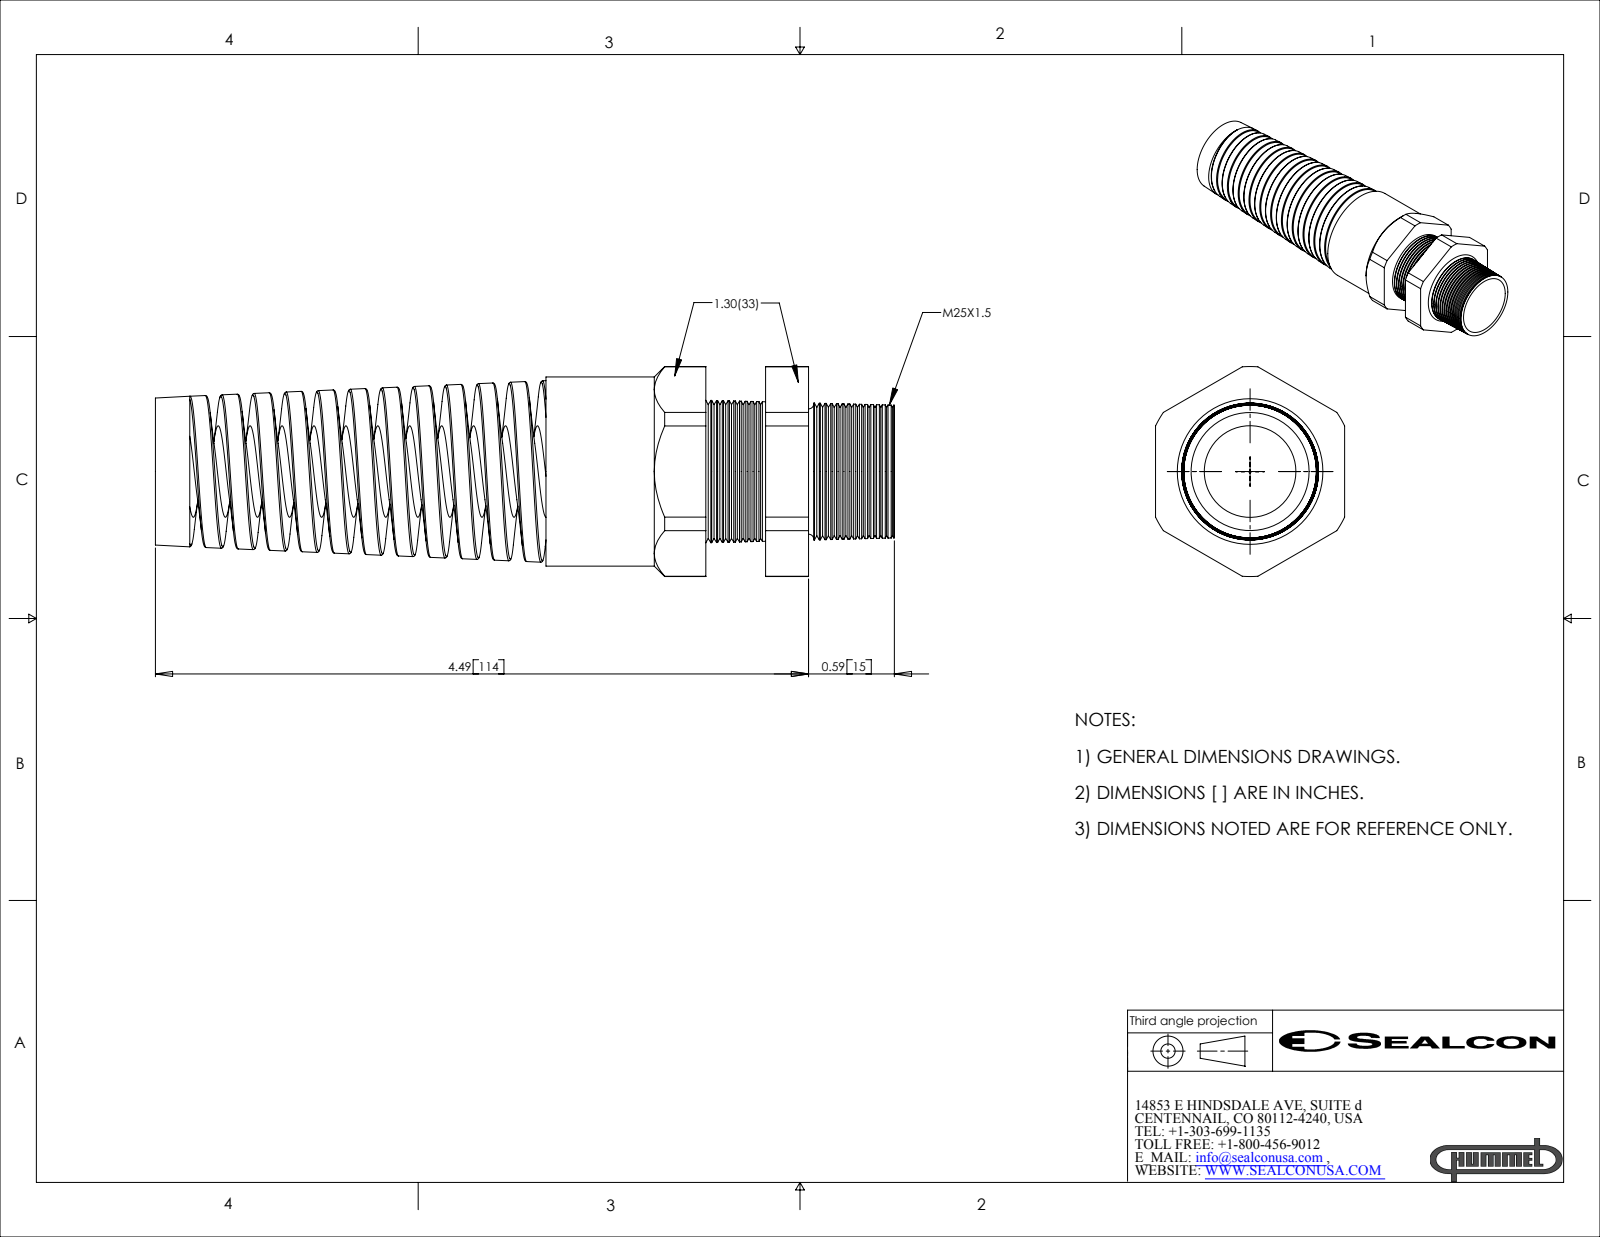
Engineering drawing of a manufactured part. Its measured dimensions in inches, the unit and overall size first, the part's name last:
Units: inches
Overall size (bounding box): 5.08 × 1.443 × 1.3
Round holes (diameter × count): ⌀0.63 ×1, ⌀0.655 ×1
Round bosses / shafts (diameter × count): ⌀1.3 ×1, ⌀0.949 ×1
Partial cylindrical surfaces — rounded edges, fillets, slot ends (radius × count): R0.721 ×1
Main face-to-face distances: 1.3, 0.411, 0.706, 0.295, 3.784, 4.195, 4.491, 2.685, 1.099, 1.51
Volume: 2.988 in³ · Surface area: 46.49 in²
Bodies: 2 solids, 264 faces (25 planar, 47 cylindrical, 192 other)
Part name (STEP PRODUCT): CF25DR-BK
STEP written by: SolidWorks 2007 (CONFIG_CONTROL_DESIGN)
